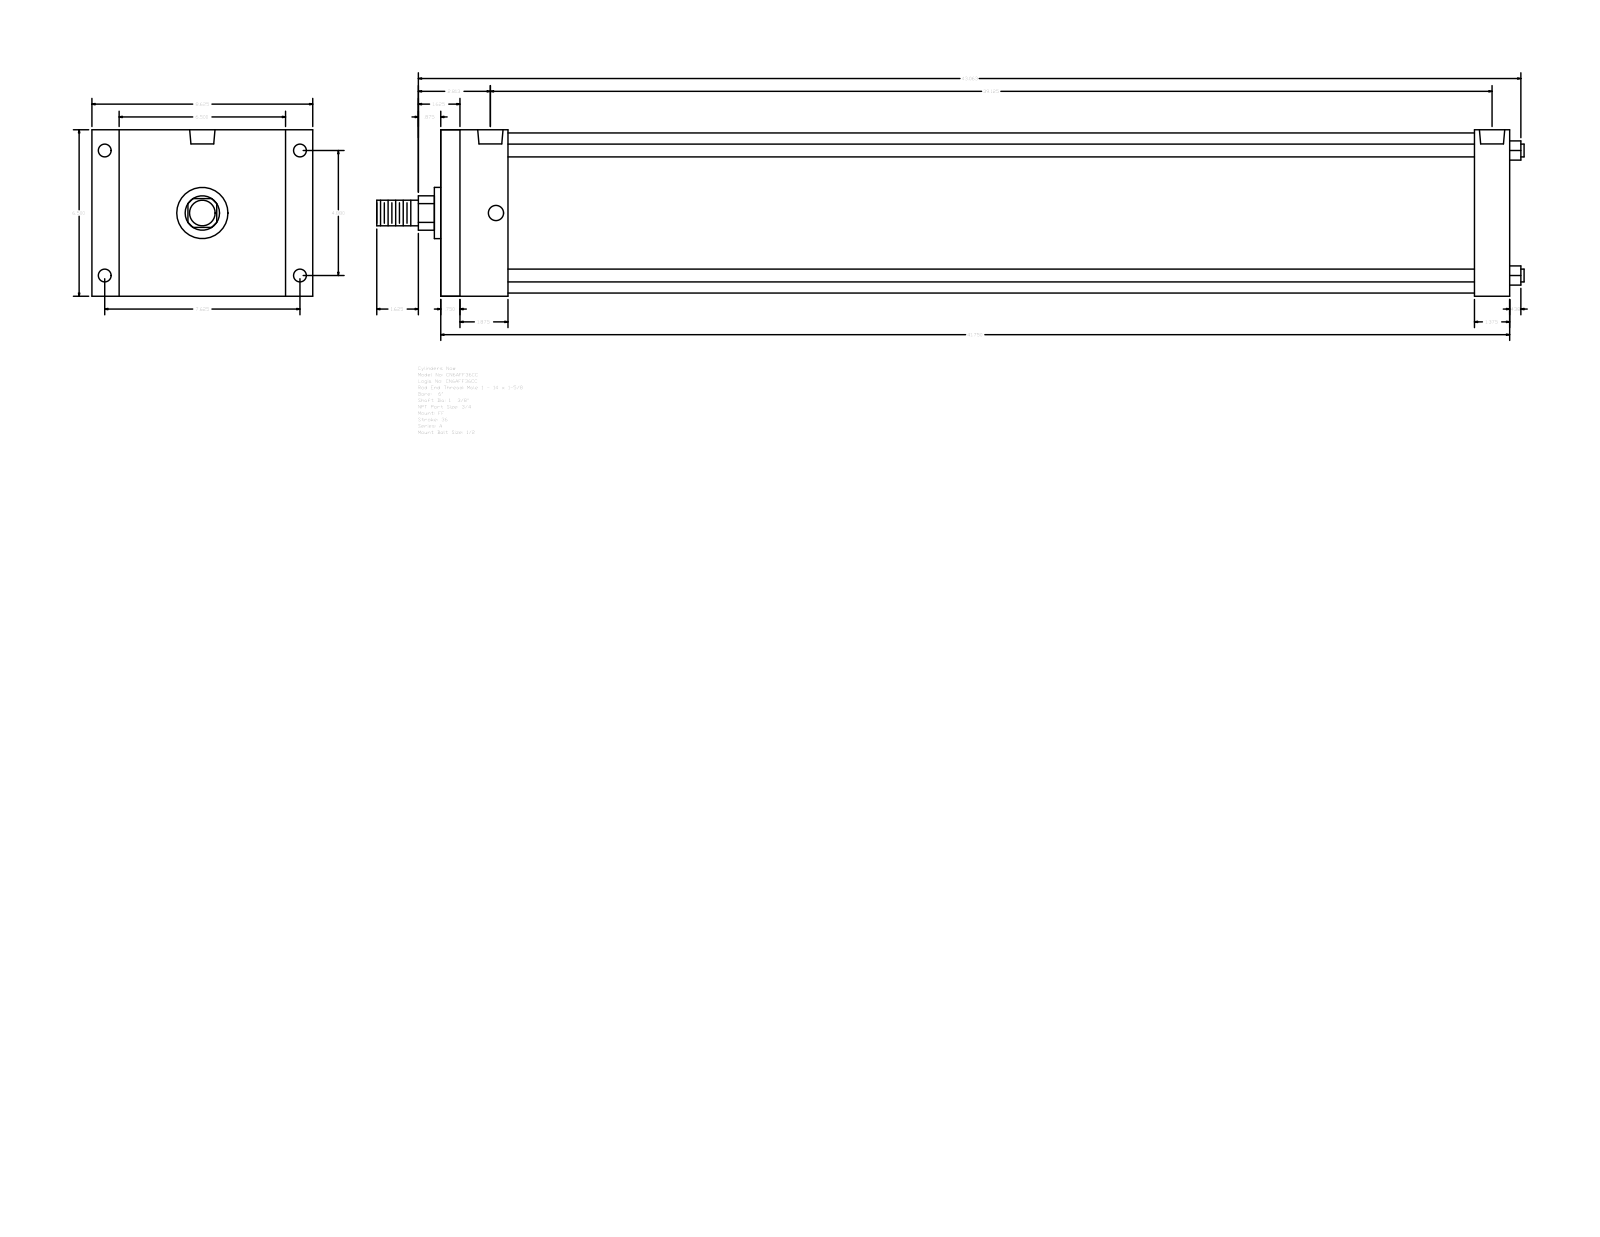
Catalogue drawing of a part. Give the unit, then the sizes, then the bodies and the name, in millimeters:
Units: millimetres
Overall size (bounding box): 1138.24 × 219.07 × 165.1
Round holes (diameter × count): ⌀12.7 ×4, ⌀15.08 ×4, ⌀25.12 ×2
Round bosses / shafts (diameter × count): ⌀12.7 ×4, ⌀158.75 ×1, ⌀50.8 ×1, ⌀34.92 ×1, ⌀25.4 ×1
Partial cylindrical surfaces — rounded edges, fillets, slot ends (radius × count): R17.06 ×1
Main face-to-face distances: 165.1, 1060.44, 19.04, 1041.4, 66.67, 47.63, 993.77, 1025.52, 1006.48, 958.85
Hole centre spacings: 5.56, 123.96, 193.68, 229.95, 982.65, 988.21, 993.77
Bodies: 0 solids, 92 faces (64 planar, 28 cylindrical, 0 other)
Part name (STEP PRODUCT): A_FF__0600_1.375
STEP written by: GSSL Pune (CONFIG_CONTROL_DESIGN)
